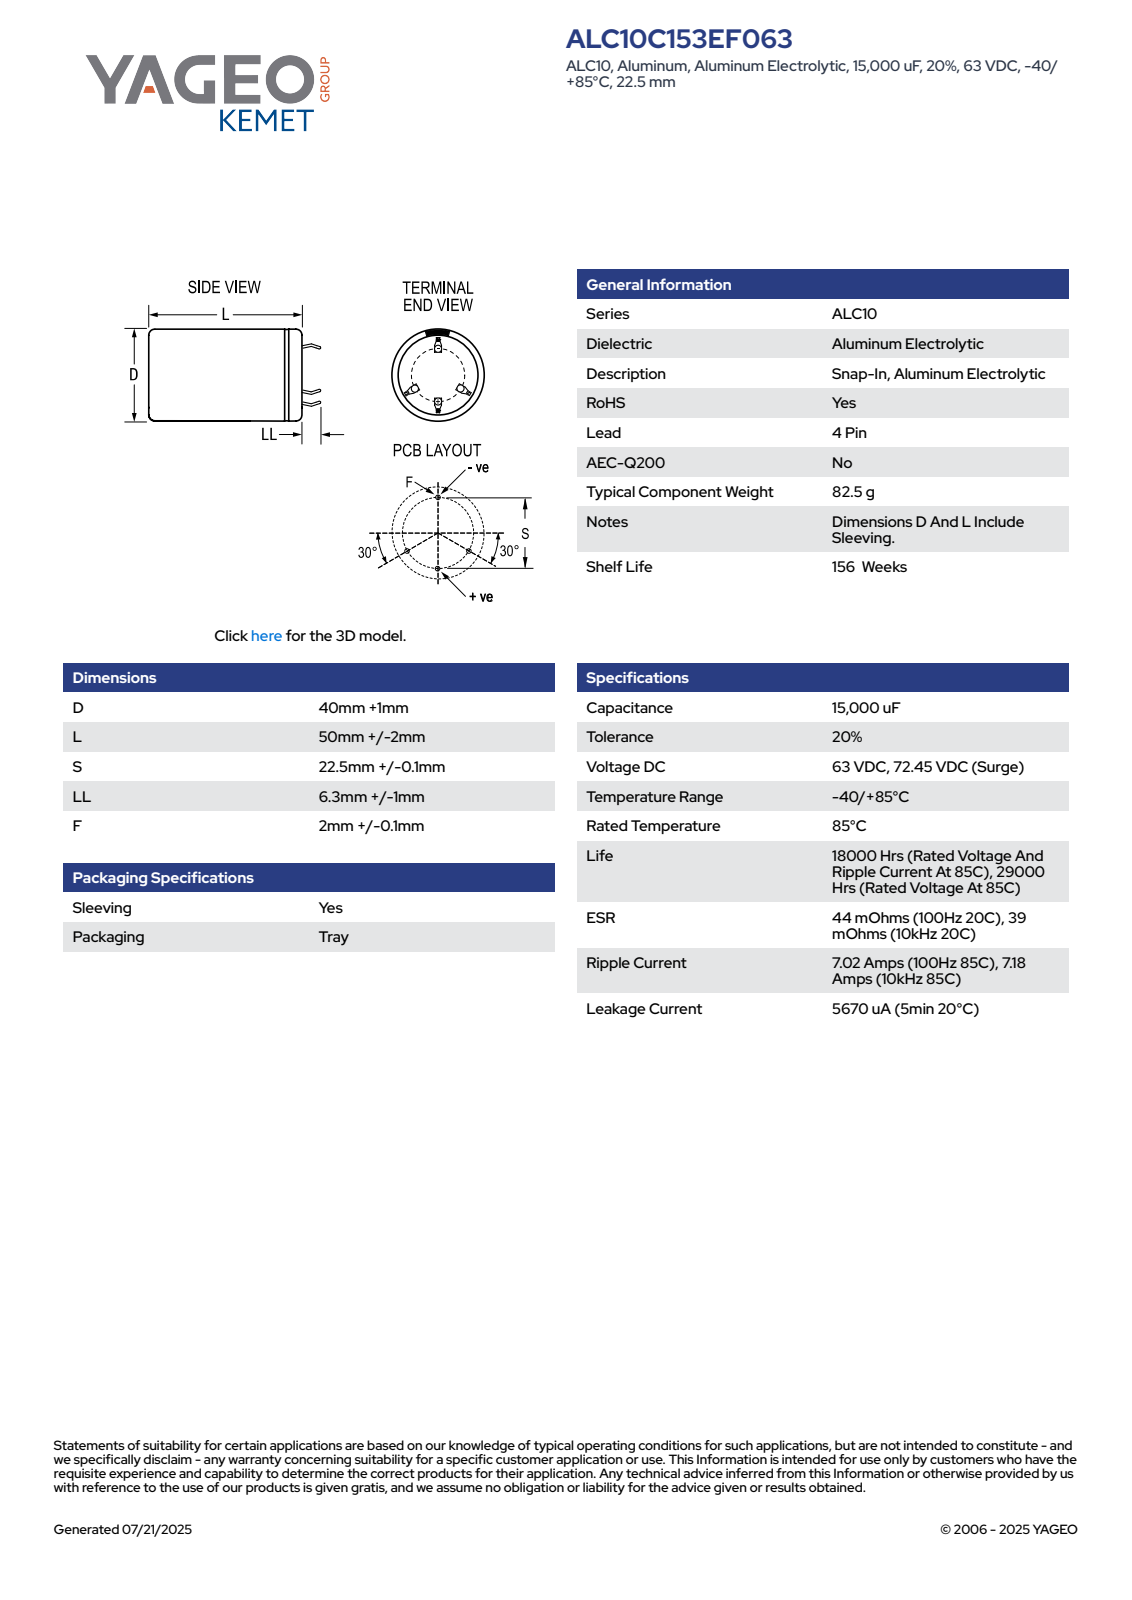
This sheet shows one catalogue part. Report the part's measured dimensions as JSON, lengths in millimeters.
{"part_name": "CARS_K4P_40X50_D41L52S22.5LL7.3F2.1", "step_written_by": "SolidWorks 2014 (AUTOMOTIVE_DESIGN)", "units": "millimeters", "bodies": {"solids": 1, "faces": 134, "planar": 80, "cylindrical": 15, "other": 39}, "overall_size": [59.29, 41, 41], "volume_mm3": 67882, "surface_area_mm2": 9384, "round_holes": [[36.28, 1]], "round_bosses_or_shafts": [[41, 1]], "partial_cylinders_radius": [[20.49, 1]], "face_to_face_distances": [51.99, 52.49, 0.5, 0.6, 0.39, 0.38, 0.75, 1.35, 20.06, 19.68]}
